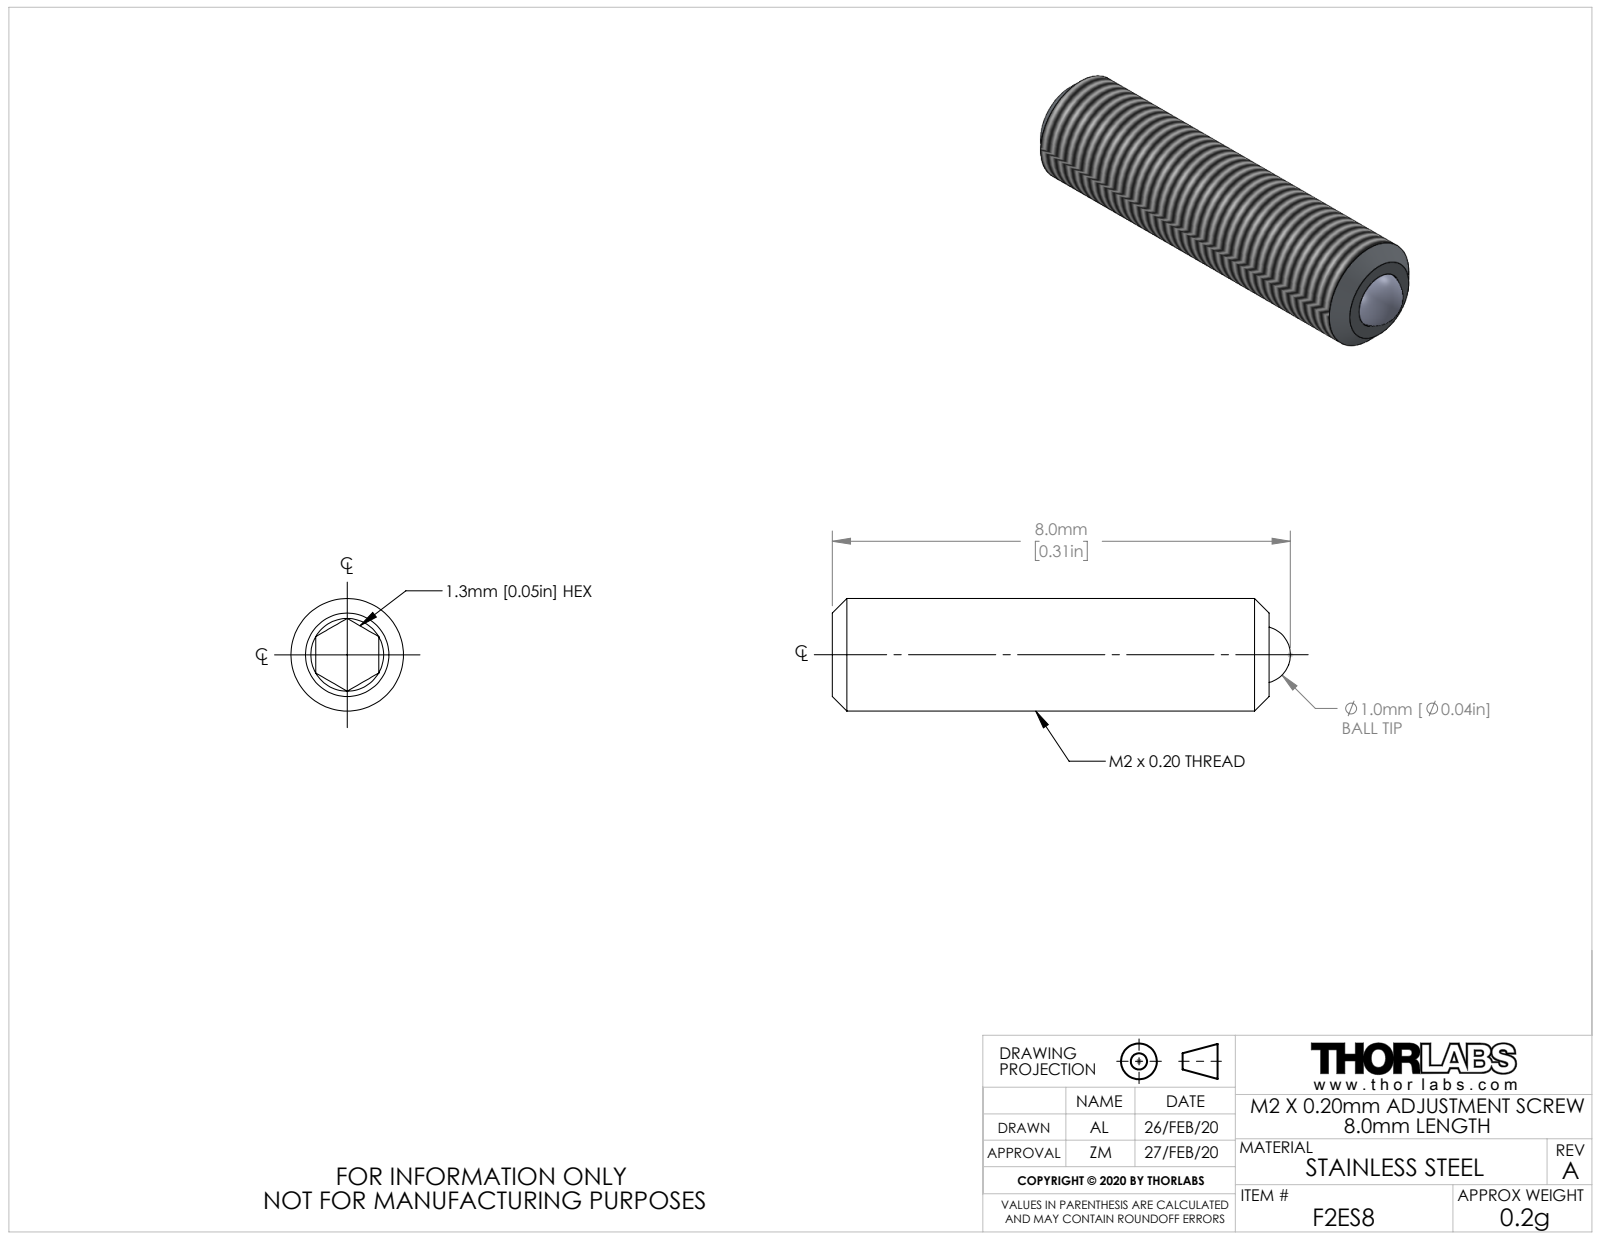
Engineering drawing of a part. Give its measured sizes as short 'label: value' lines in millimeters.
name: TTN210088-E0W
written by: SolidWorks 2018 (AUTOMOTIVE_DESIGN)
unit: mm
bodies: 2 solids, 28 faces (9 planar, 4 cylindrical, 15 other)
size: 8 × 2 × 2
volume: 20 mm³; area: 63 mm²
holes: 1× ⌀1
bosses: 1× ⌀2
face distances: 1.1, 5.6, 2, 7.6
